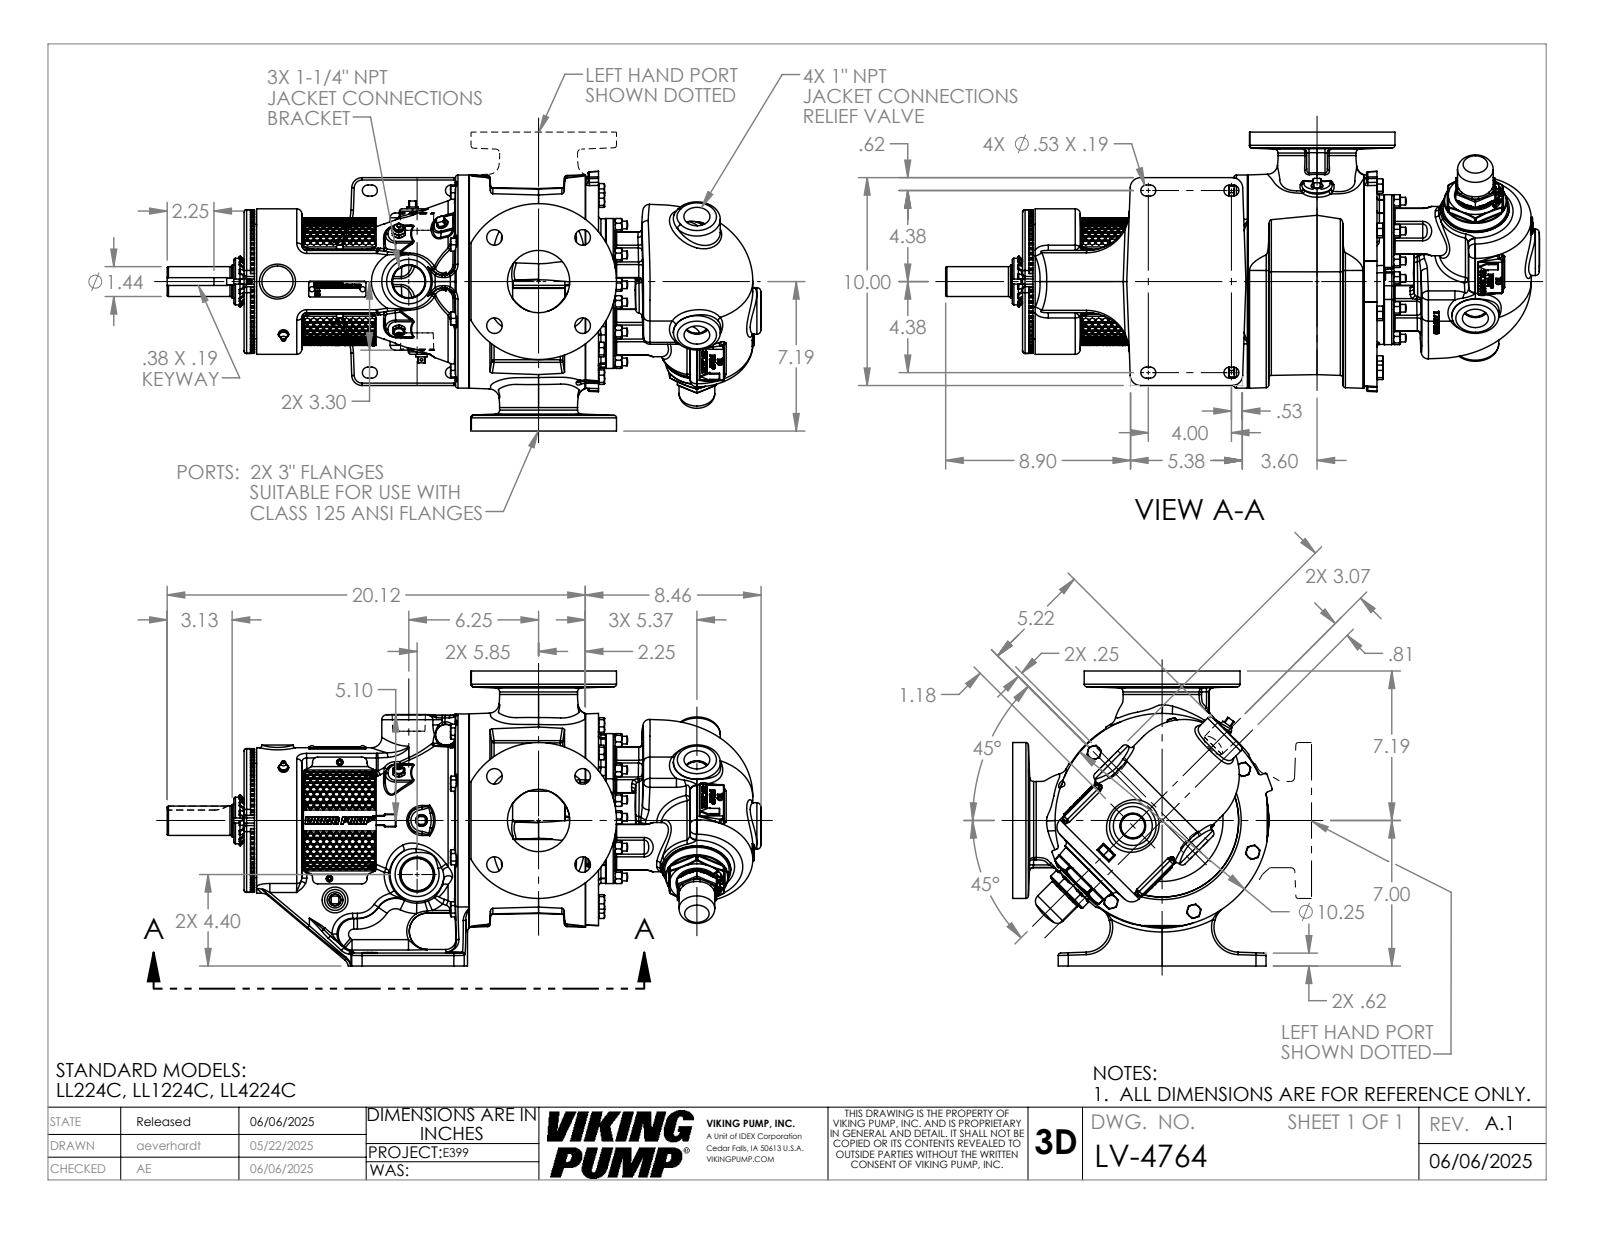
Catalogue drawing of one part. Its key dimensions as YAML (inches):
part_name: "LV-4764"
step_written_by: "SolidWorks 2024 (AUTOMOTIVE_DESIGN)"
units: inches
bodies: {solids: 1, faces: 5260, planar: 1678, cylindrical: 877, other: 2705}
overall_size: [28.579, 14.19, 12.492]
volume: 1190
surface_area: 1604
round_holes:
  - {diameter: 0.75, count: 8}
  - {diameter: 1.094, count: 8}
  - {diameter: 0.199, count: 6}
  - {diameter: 0.25, count: 6}
  - {diameter: 0.159, count: 3}
  - {diameter: 0.266, count: 2}
  - {diameter: 0.313, count: 2}
  - {diameter: 0.063, count: 1}
  - {diameter: 0.125, count: 1}
  - {diameter: 0.453, count: 1}
  - {diameter: 1.577, count: 1}
  - {diameter: 1.593, count: 1}
round_bosses_or_shafts:
  - {diameter: 0.625, count: 9}
  - {diameter: 0.369, count: 8}
  - {diameter: 0.625, count: 6}
  - {diameter: 0.437, count: 3}
  - {diameter: 0.312, count: 3}
  - {diameter: 7.5, count: 2}
  - {diameter: 3.75, count: 2}
  - {diameter: 3.5, count: 2}
partial_cylinders:
  - {radius: 0.063, count: 109}
  - {radius: 0.12, count: 105}
  - {radius: 0.069, count: 74}
  - {radius: 0.5, count: 34}
  - {radius: 0.03, count: 24}
  - {radius: 0.24, count: 16}
  - {radius: 0.19, count: 14}
  - {radius: 0.06, count: 12}
face_to_face_distances: [14.19, 14.307, 3.537, 10.77, 0.5, 2.25, 1.5, 2.143, 5.68, 16.45]
hole_center_spacings: [3, 4.243, 1.375, 2.18, 3.609, 4.446, 4.625, 6.404]
